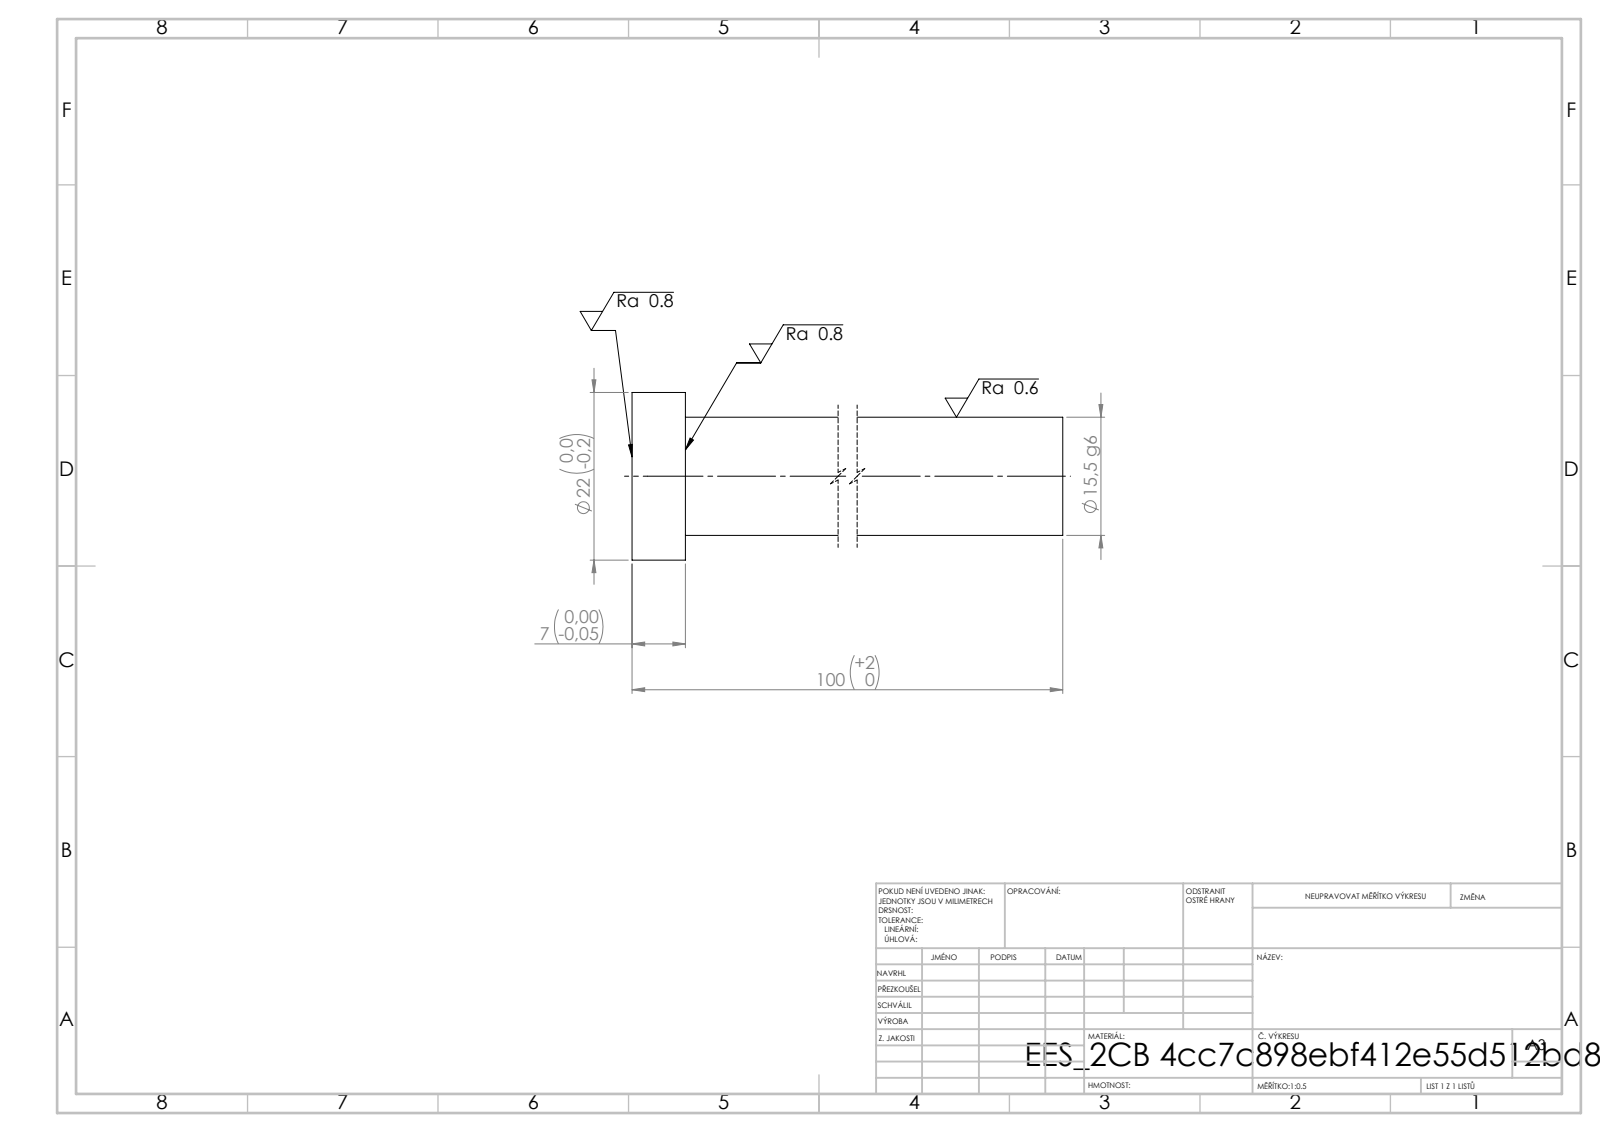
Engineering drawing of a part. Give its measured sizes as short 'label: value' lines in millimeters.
written by: SolidWorks 2019 (CONFIG_CONTROL_DESIGN)
unit: mm
bodies: 1 solid, 7 faces (3 planar, 4 cylindrical, 0 other)
size: 100 × 22 × 22
volume: 20 209 mm³; area: 5 773 mm²
bosses: 1× ⌀22, 1× ⌀15.5
face distances: 7, 100, 93
